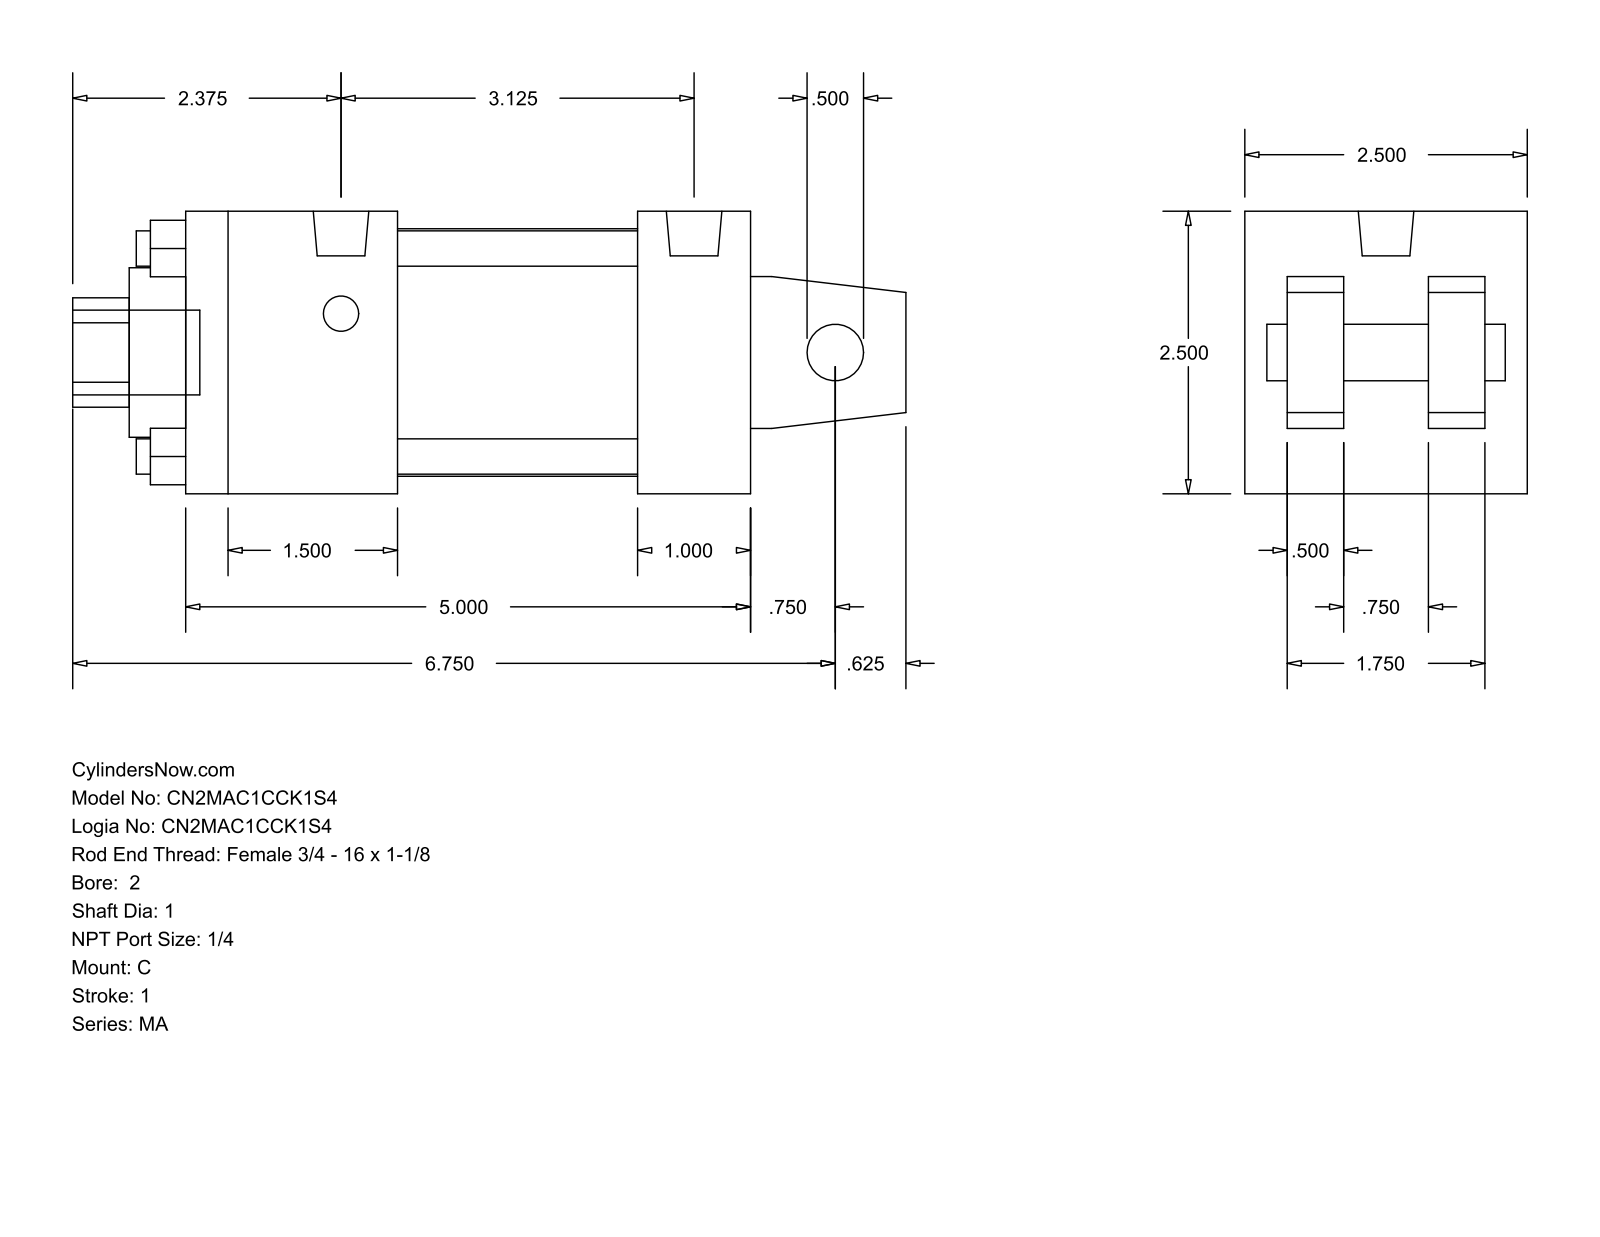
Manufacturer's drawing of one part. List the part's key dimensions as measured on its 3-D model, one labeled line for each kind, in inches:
Part name (STEP PRODUCT): MA_C__0200_1
STEP written by: GSSL Pune (CONFIG_CONTROL_DESIGN)
Units: inches
Bodies: 0 solids, 103 faces (76 planar, 27 cylindrical, 0 other)
Overall size (bounding box): 7.375 × 2.5 × 2.5
Round holes (diameter × count): ⌀0.313 ×4, ⌀0.5 ×1, ⌀1 ×1, ⌀1.5 ×1, ⌀2.19 ×1
Round bosses / shafts (diameter × count): ⌀0.313 ×4, ⌀0.492 ×2, ⌀0.75 ×1
Partial cylindrical surfaces — rounded edges, fillets, slot ends (radius × count): R0.484 ×1
Main face-to-face distances: 2.5, 0.5, 5, 0.875, 1.625, 0.375, 2.125, 1.25, 1.875, 1
Hole centre spacings: 1.301, 1.84, 2.602
